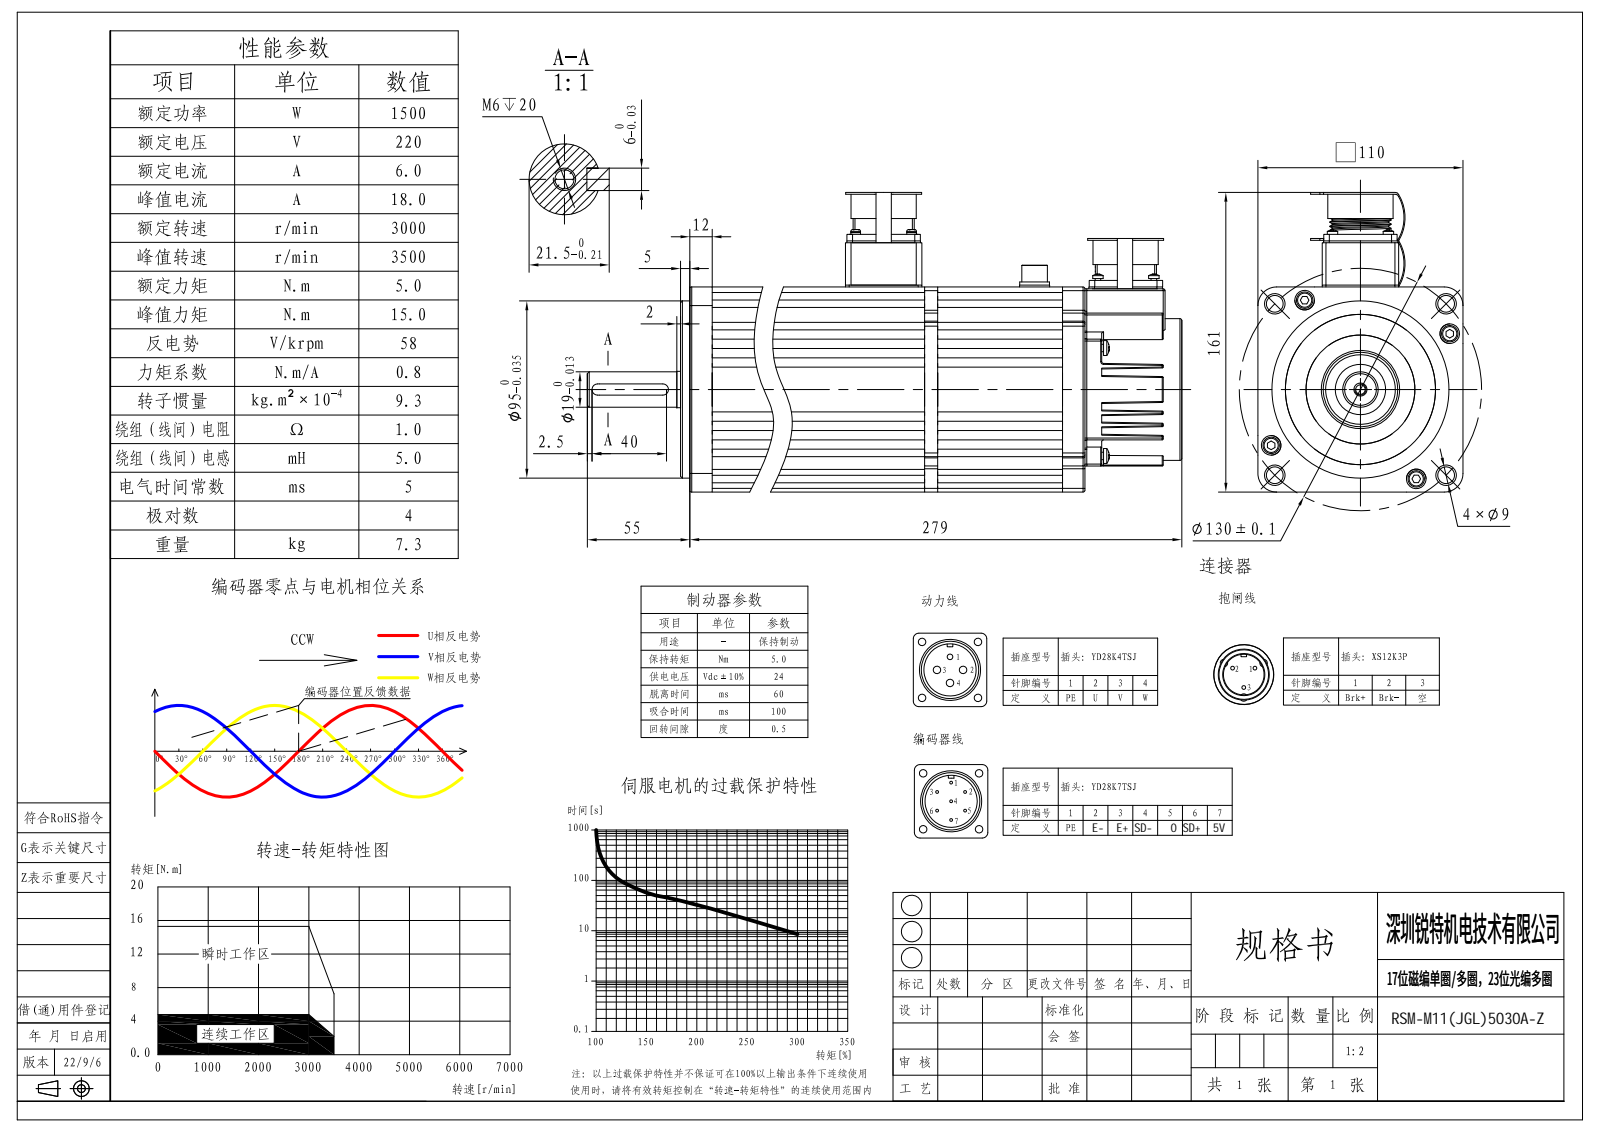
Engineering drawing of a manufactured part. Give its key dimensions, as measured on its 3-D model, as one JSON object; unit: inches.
{"part_name": "110后端盖（带钢套）; 110前端盖（不带钢套）-米格外观; cross recessed pan head screws gb_GB_CROSS_SCREWS_TYPE1 M3X12-12 H type-N; 110前端盖（带钢套） (+8 more)", "step_written_by": "SolidWorks 2018 (CONFIG_CONTROL_DESIGN)", "units": "inches", "bodies": {"solids": 45, "faces": 3847, "planar": 1373, "cylindrical": 1590, "other": 884}, "overall_size": [13.15, 6.327, 4.331], "volume_in3": 59.39, "surface_area_in2": 825.5, "round_holes": [[0.059, 15], [0.098, 11], [0.138, 8], [0.157, 8], [0.165, 7], [0.13, 6], [0.197, 5], [0.177, 4], [0.22, 4], [0.236, 4], [0.256, 4], [0.354, 4]], "round_bosses_or_shafts": [[0.098, 15], [0.118, 11], [0.157, 8], [0.335, 4], [0.22, 4], [0.205, 4], [0.197, 4], [0.189, 4]], "partial_cylinders_radius": [[0.039, 74], [0.02, 56], [0.079, 41], [0.012, 32], [0.118, 29], [0.059, 6], [0.069, 5], [0.148, 4]], "face_to_face_distances": [0.197, 0.472, 0.079, 0.276, 4.331, 0.118, 0.059, 3.228, 0.157, 2.205], "hole_center_spacings": [0.835, 1.181, 0.669, 1.048, 2.772, 0.406, 0.702, 0.827]}
